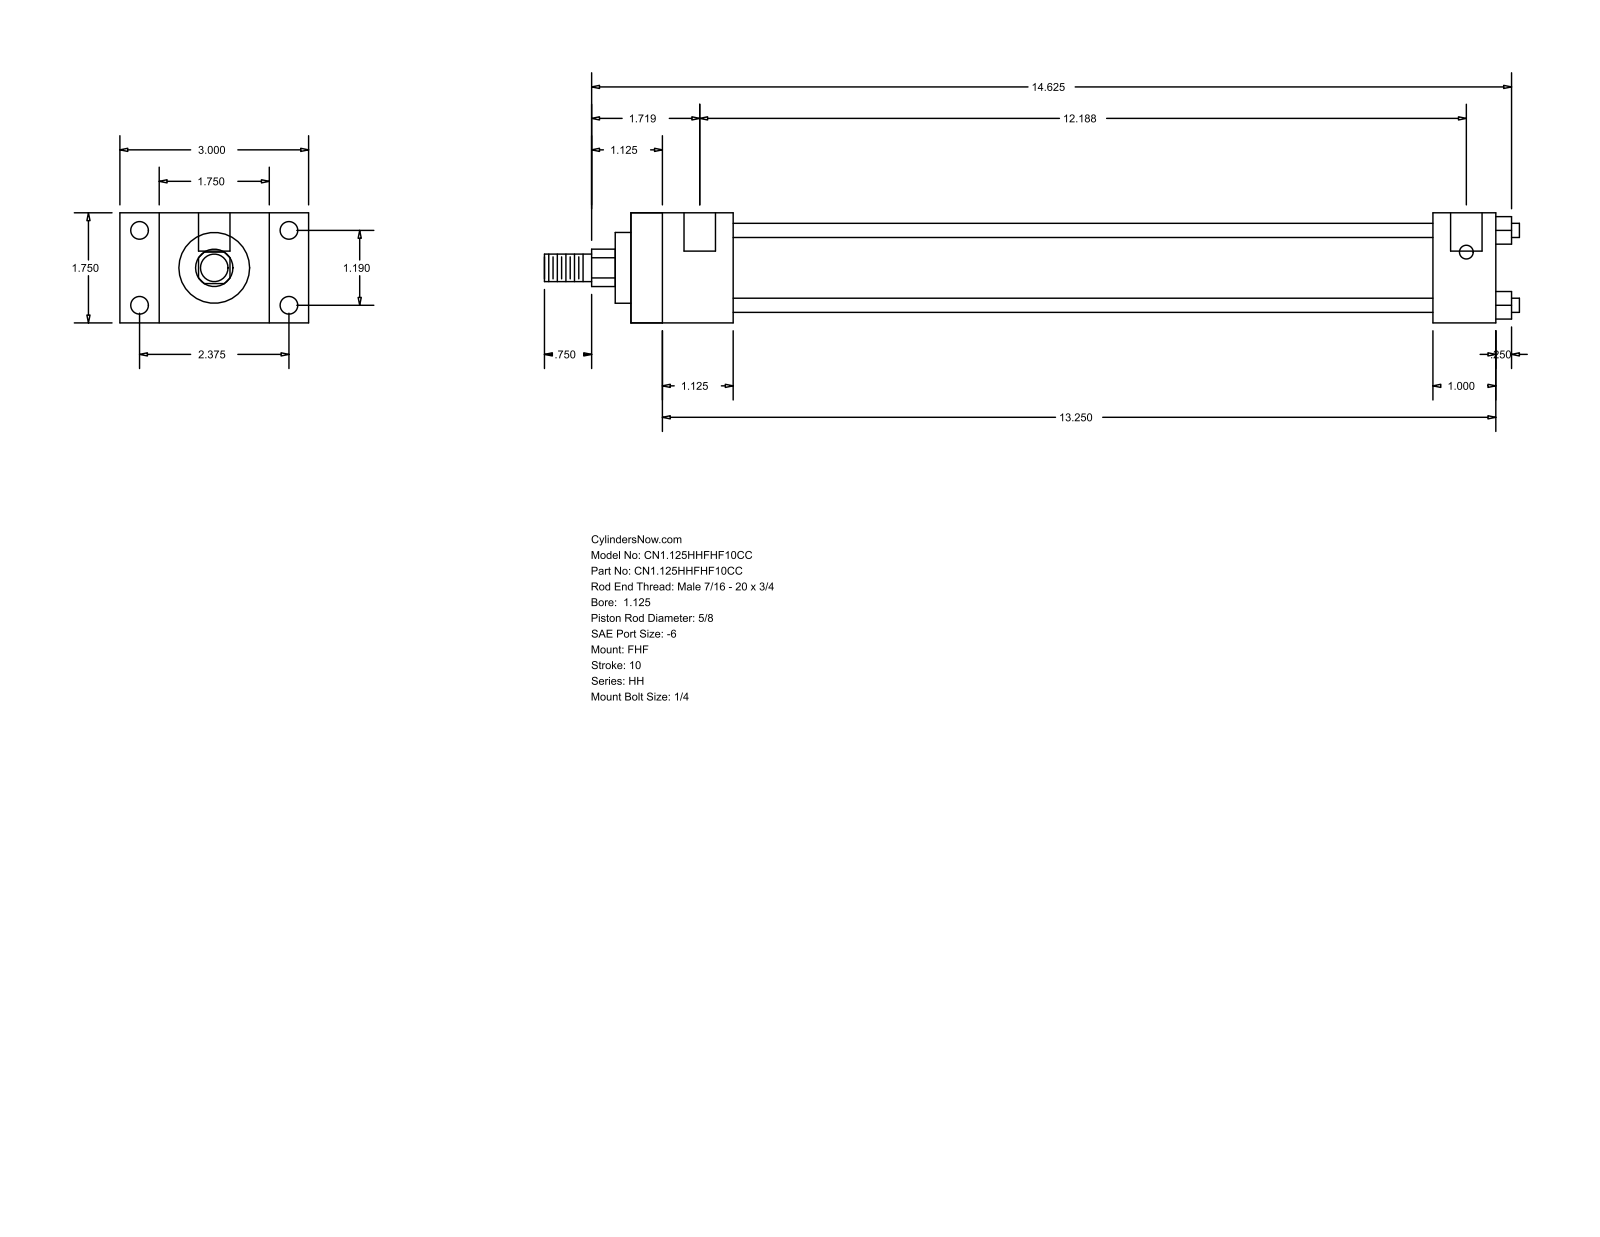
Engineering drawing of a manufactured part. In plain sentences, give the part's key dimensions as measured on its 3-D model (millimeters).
The part is named "HH_FHF__0112_0.625". Its 3-D file was written by "GSSL Pune (CONFIG_CONTROL_DESIGN)". It is 0 solids with 88 faces: 60 planar, 28 cylindrical and 0 other. Overall it measures 393.7 by 76.2 by 44.45 millimeters. Round holes: 4 of diameter 5.56, 4 of diameter 7.14, 2 of diameter 12.7. Round bosses or shafts: 4 of diameter 5.71, 1 of diameter 34.92, 1 of diameter 28.57, 1 of diameter 15.88, 1 of diameter 11.11. Partial cylindrical surfaces (rounded edges, fillets, slot ends): 1 of radius 7.54. The main face-to-face distances are 44.46, 15.87, 60.33, 41.27, 76.2, 349.24, 307.97, 323.85, 282.58, 25.39. The hole center spacings are 30.22, 60.32, 67.47, 306.39, 3.17, 309.56.
